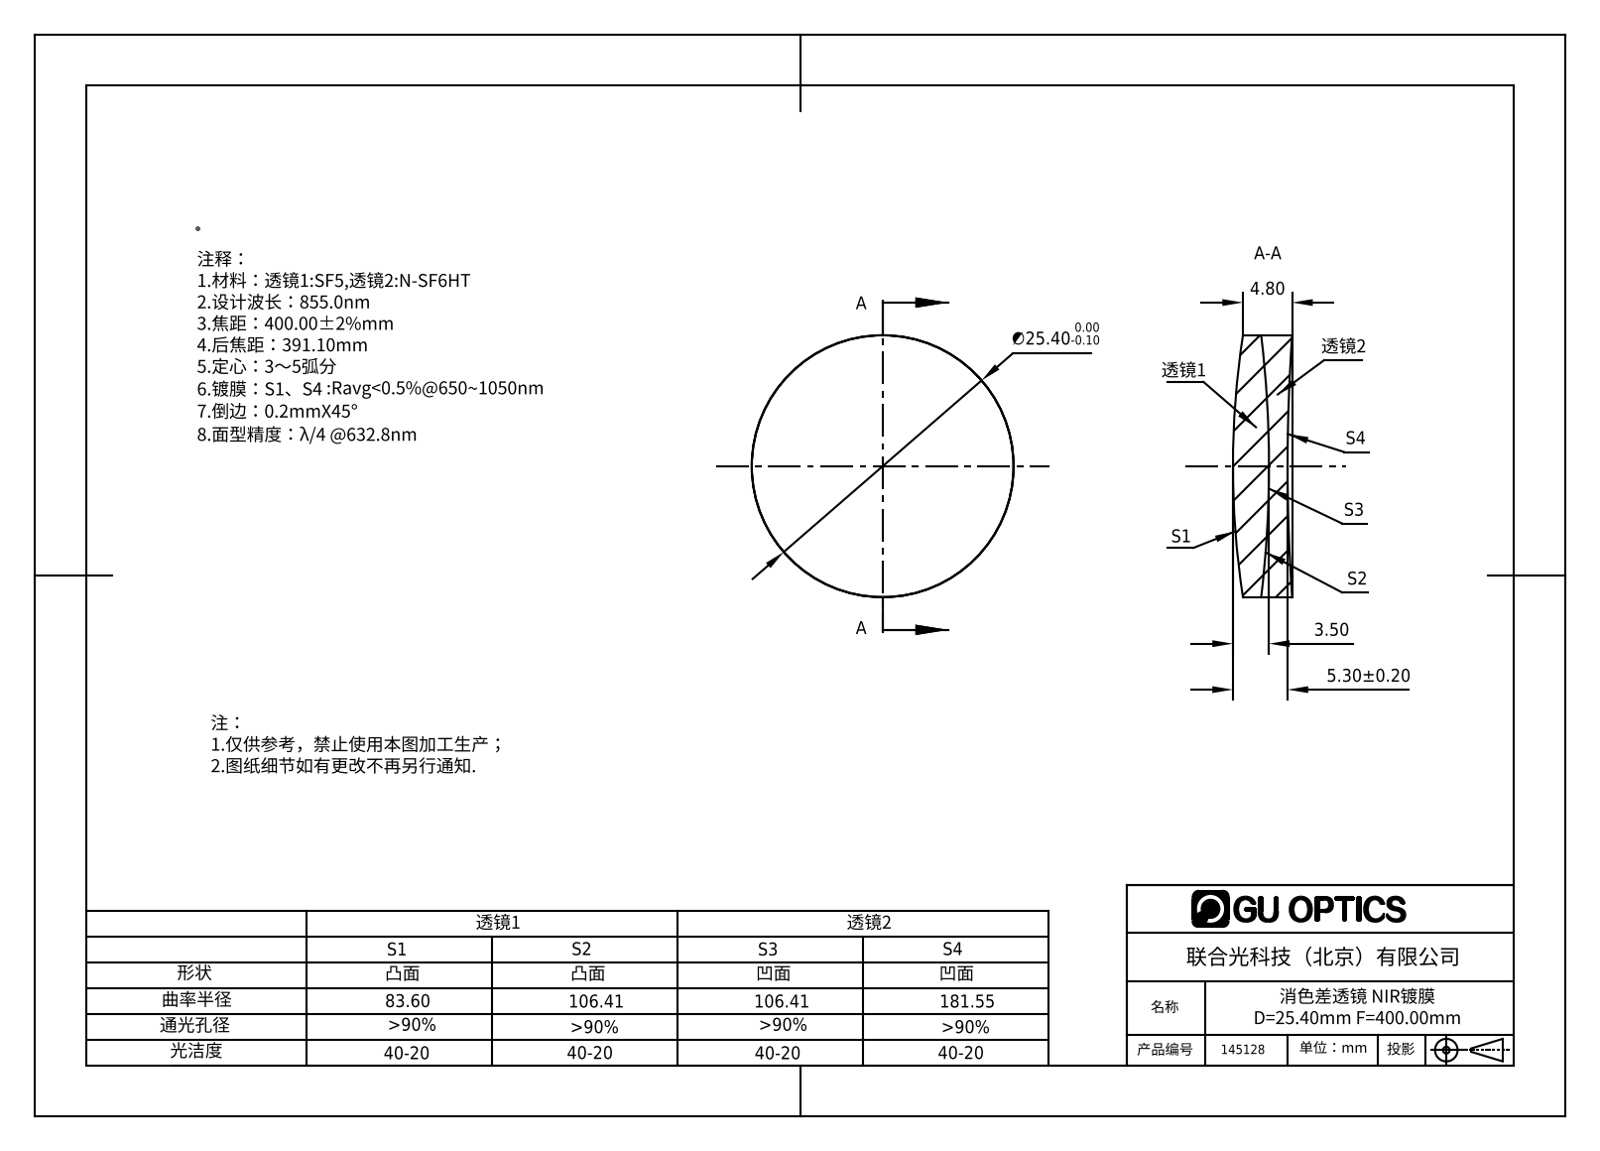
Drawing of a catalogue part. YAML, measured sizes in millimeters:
part_name: "145128"
step_written_by: "SolidWorks 2016 (AUTOMOTIVE_DESIGN)"
units: millimeters
bodies: {solids: 2, faces: 12, planar: 0, cylindrical: 4, other: 8}
overall_size: [25.4, 25.4, 5.75]
volume: 2553
surface_area: 2415
round_bosses_or_shafts:
  - {diameter: 25.4, count: 1}
